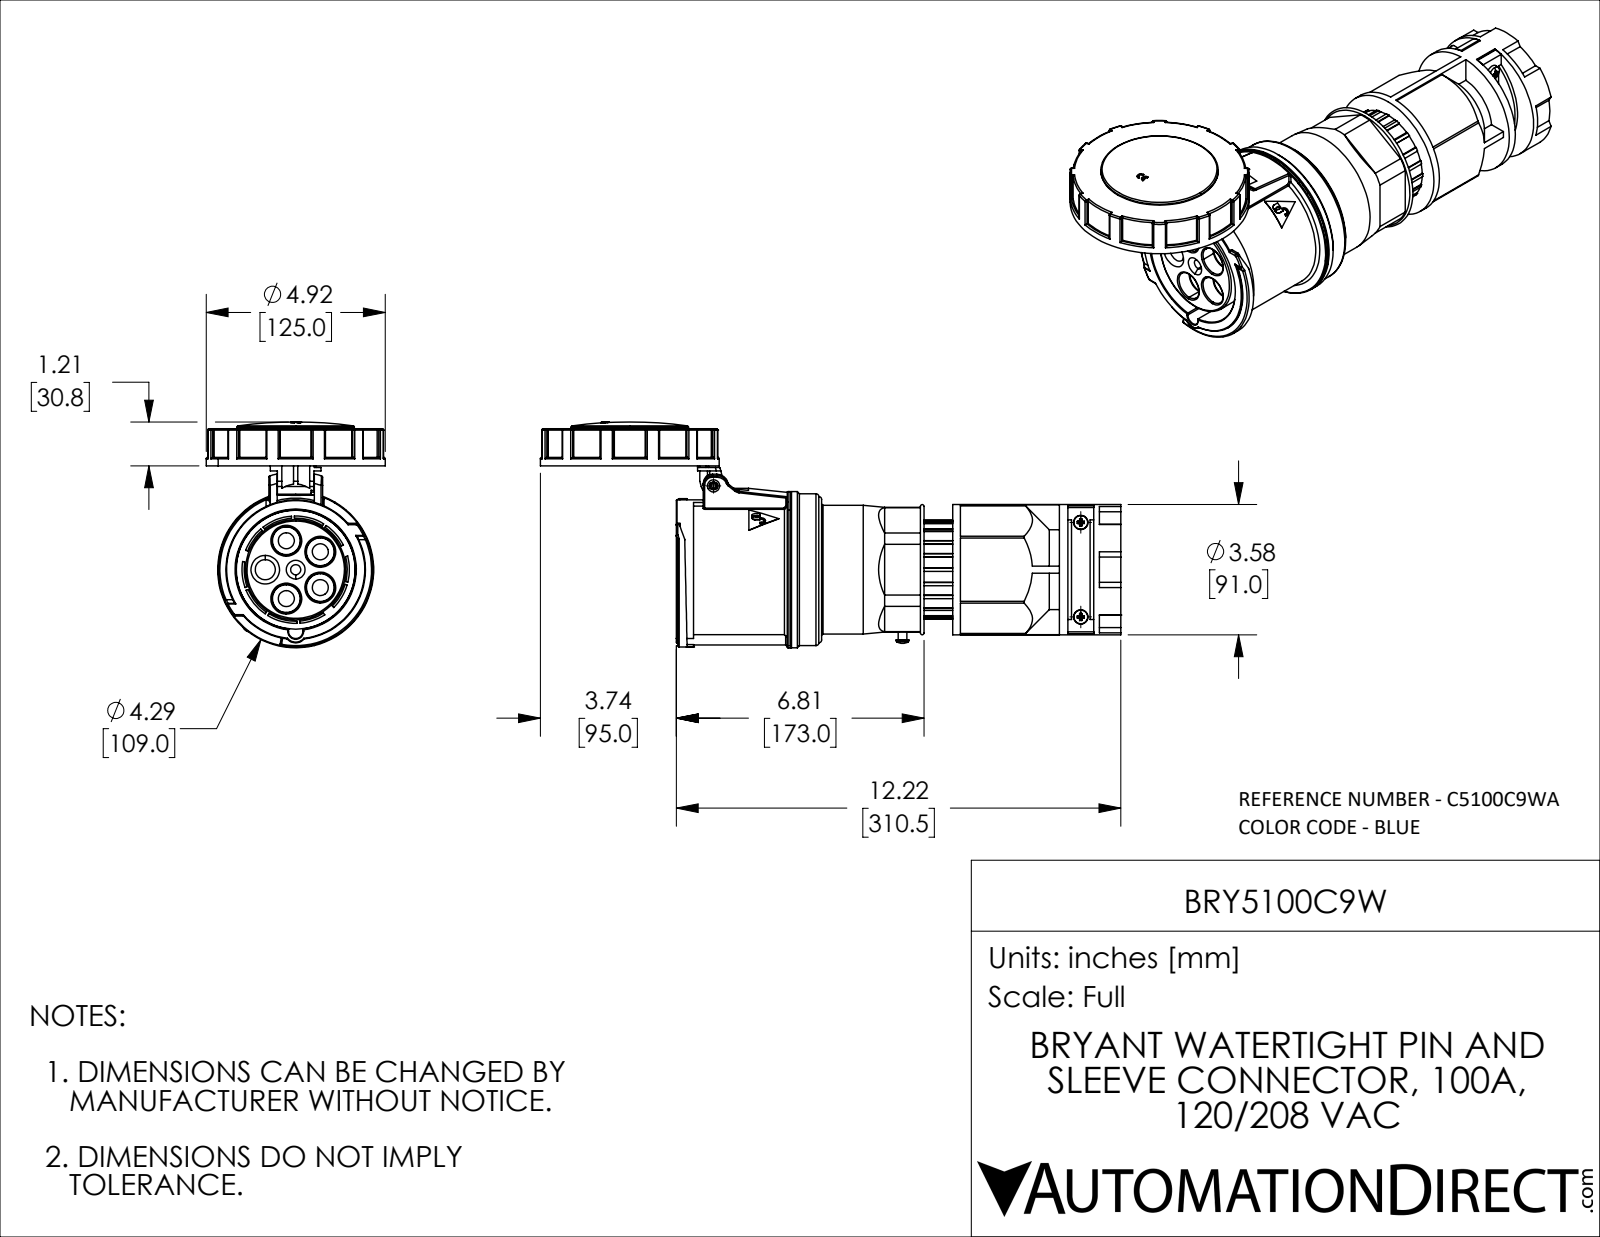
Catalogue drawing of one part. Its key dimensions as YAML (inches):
part_name: "BRY5100C9W"
step_written_by: "SolidWorks 2021 (CONFIG_CONTROL_DESIGN)"
units: inches
bodies: {solids: 7, faces: 1245, planar: 454, cylindrical: 438, other: 353}
overall_size: [15.965, 6.207, 4.921]
volume: 104
surface_area: 411.2
round_holes:
  - {diameter: 0.441, count: 4}
  - {diameter: 0.787, count: 4}
  - {diameter: 0.28, count: 1}
  - {diameter: 0.335, count: 1}
  - {diameter: 0.551, count: 1}
  - {diameter: 1.969, count: 1}
  - {diameter: 2.953, count: 1}
  - {diameter: 3.189, count: 1}
  - {diameter: 4.528, count: 1}
round_bosses_or_shafts:
  - {diameter: 0.197, count: 3}
  - {diameter: 0.925, count: 2}
  - {diameter: 4.921, count: 1}
  - {diameter: 4.291, count: 1}
  - {diameter: 4.177, count: 1}
  - {diameter: 3.839, count: 1}
  - {diameter: 3.646, count: 1}
  - {diameter: 3.583, count: 1}
partial_cylinders:
  - {radius: 0.039, count: 75}
  - {radius: 0.02, count: 5}
  - {radius: 0.079, count: 4}
  - {radius: 0.118, count: 4}
  - {radius: 0.197, count: 4}
  - {radius: 0.463, count: 3}
  - {radius: 0.069, count: 2}
  - {radius: 0.098, count: 2}
face_to_face_distances: [3.13, 3.957, 4.665, 0.709, 0.906, 0.098, 0.118, 1.063, 0.236, 0.827]
hole_center_spacings: [0.837, 0.983, 1.591]
